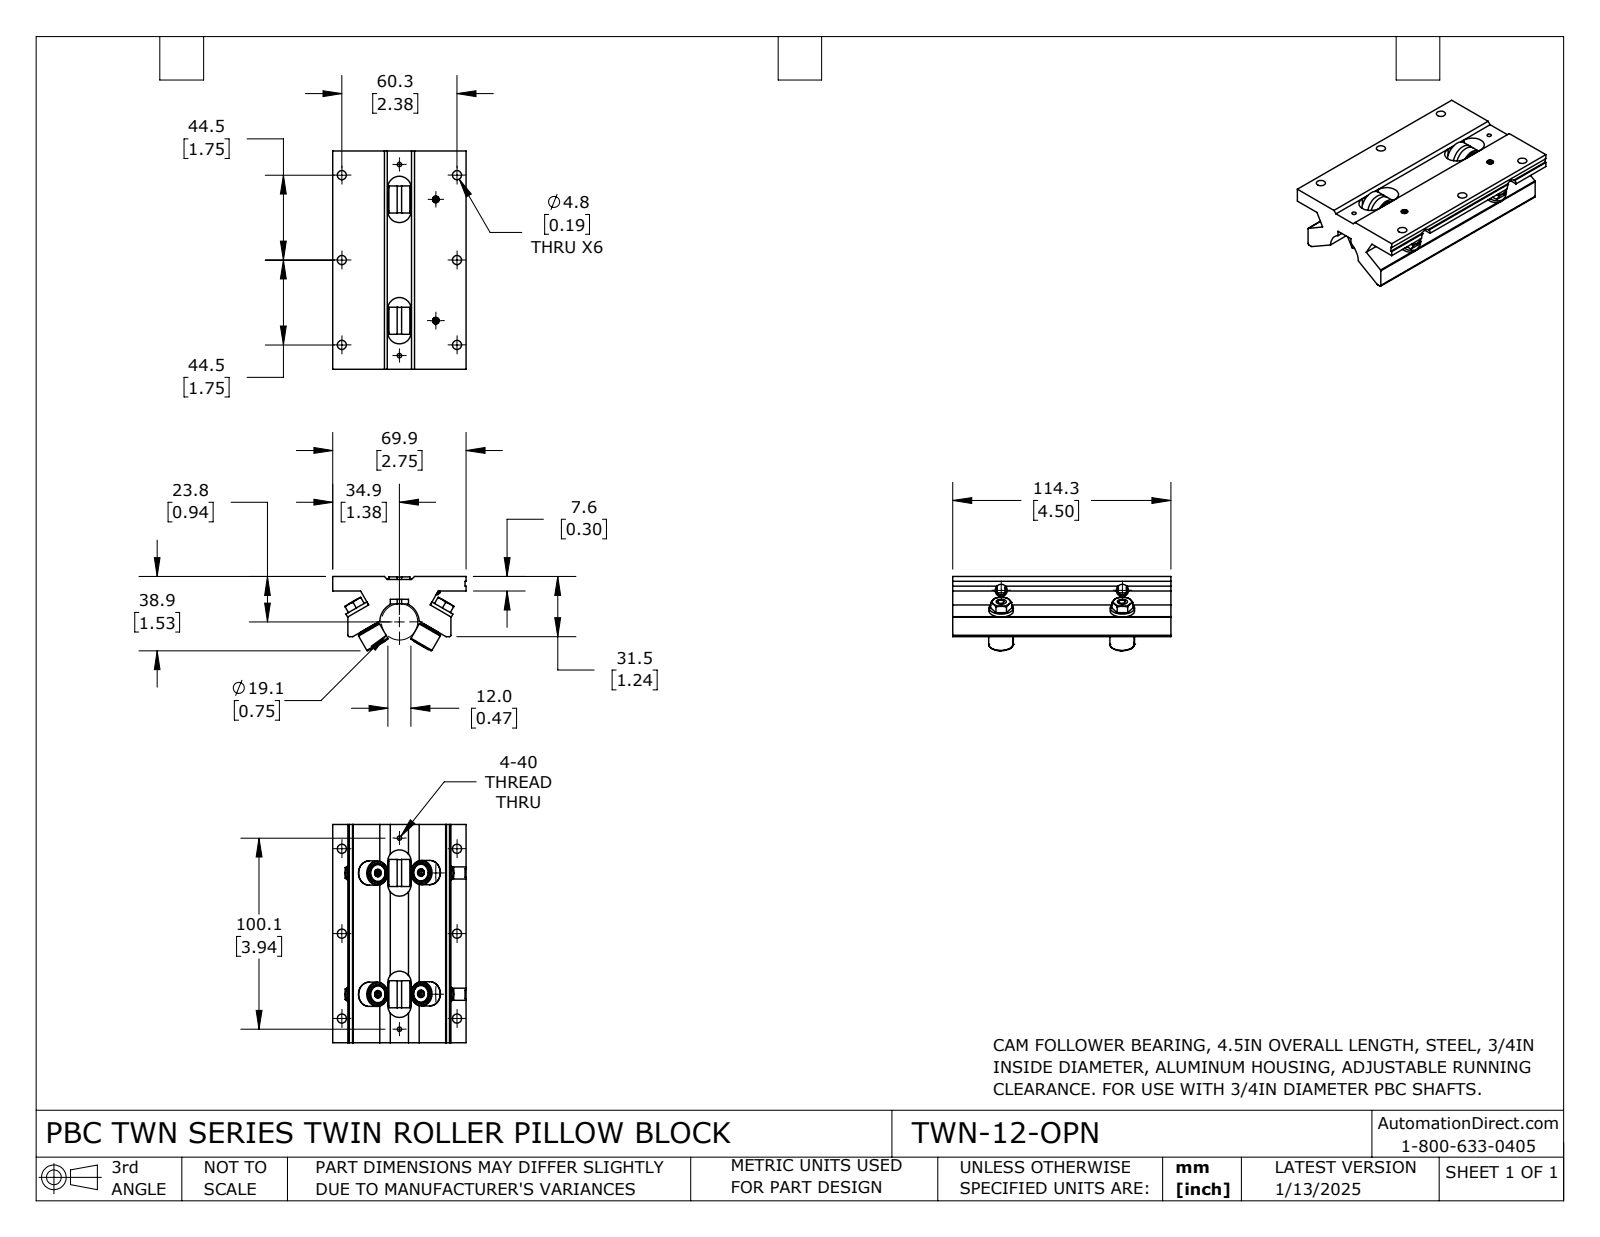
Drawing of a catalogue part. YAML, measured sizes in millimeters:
part_name: "TWN-12-OPN"
step_written_by: "SolidWorks 2023 (CONFIG_CONTROL_DESIGN)"
units: millimeters
bodies: {solids: 19, faces: 580, planar: 238, cylindrical: 182, other: 160}
overall_size: [114.3, 69.9, 38.9]
volume: 133800
surface_area: 43000
round_holes:
  - {diameter: 4.7, count: 6}
  - {diameter: 3.3, count: 4}
  - {diameter: 3.8, count: 4}
  - {diameter: 10.1, count: 4}
  - {diameter: 2.3, count: 2}
  - {diameter: 3.5, count: 2}
  - {diameter: 4, count: 2}
  - {diameter: 4.8, count: 2}
  - {diameter: 4.9, count: 2}
  - {diameter: 5, count: 2}
  - {diameter: 5, count: 2}
  - {diameter: 5.1, count: 2}
round_bosses_or_shafts:
  - {diameter: 12.7, count: 6}
  - {diameter: 9.4, count: 4}
  - {diameter: 14.1, count: 2}
  - {diameter: 12.1, count: 2}
  - {diameter: 6.4, count: 2}
  - {diameter: 5.1, count: 2}
  - {diameter: 5, count: 2}
  - {diameter: 4.8, count: 2}
partial_cylinders:
  - {radius: 0.8, count: 4}
  - {radius: 6.1, count: 3}
  - {radius: 0.4, count: 2}
  - {radius: 6.2, count: 1}
  - {radius: 10.3, count: 1}
face_to_face_distances: [10.3, 7.6, 7.9, 61.9, 114.3, 54, 6.1, 1.5, 4.3, 10.4]
hole_center_spacings: [63.5, 30.7, 44.5, 58.4, 74.9, 99.2, 60.3, 16.9]
